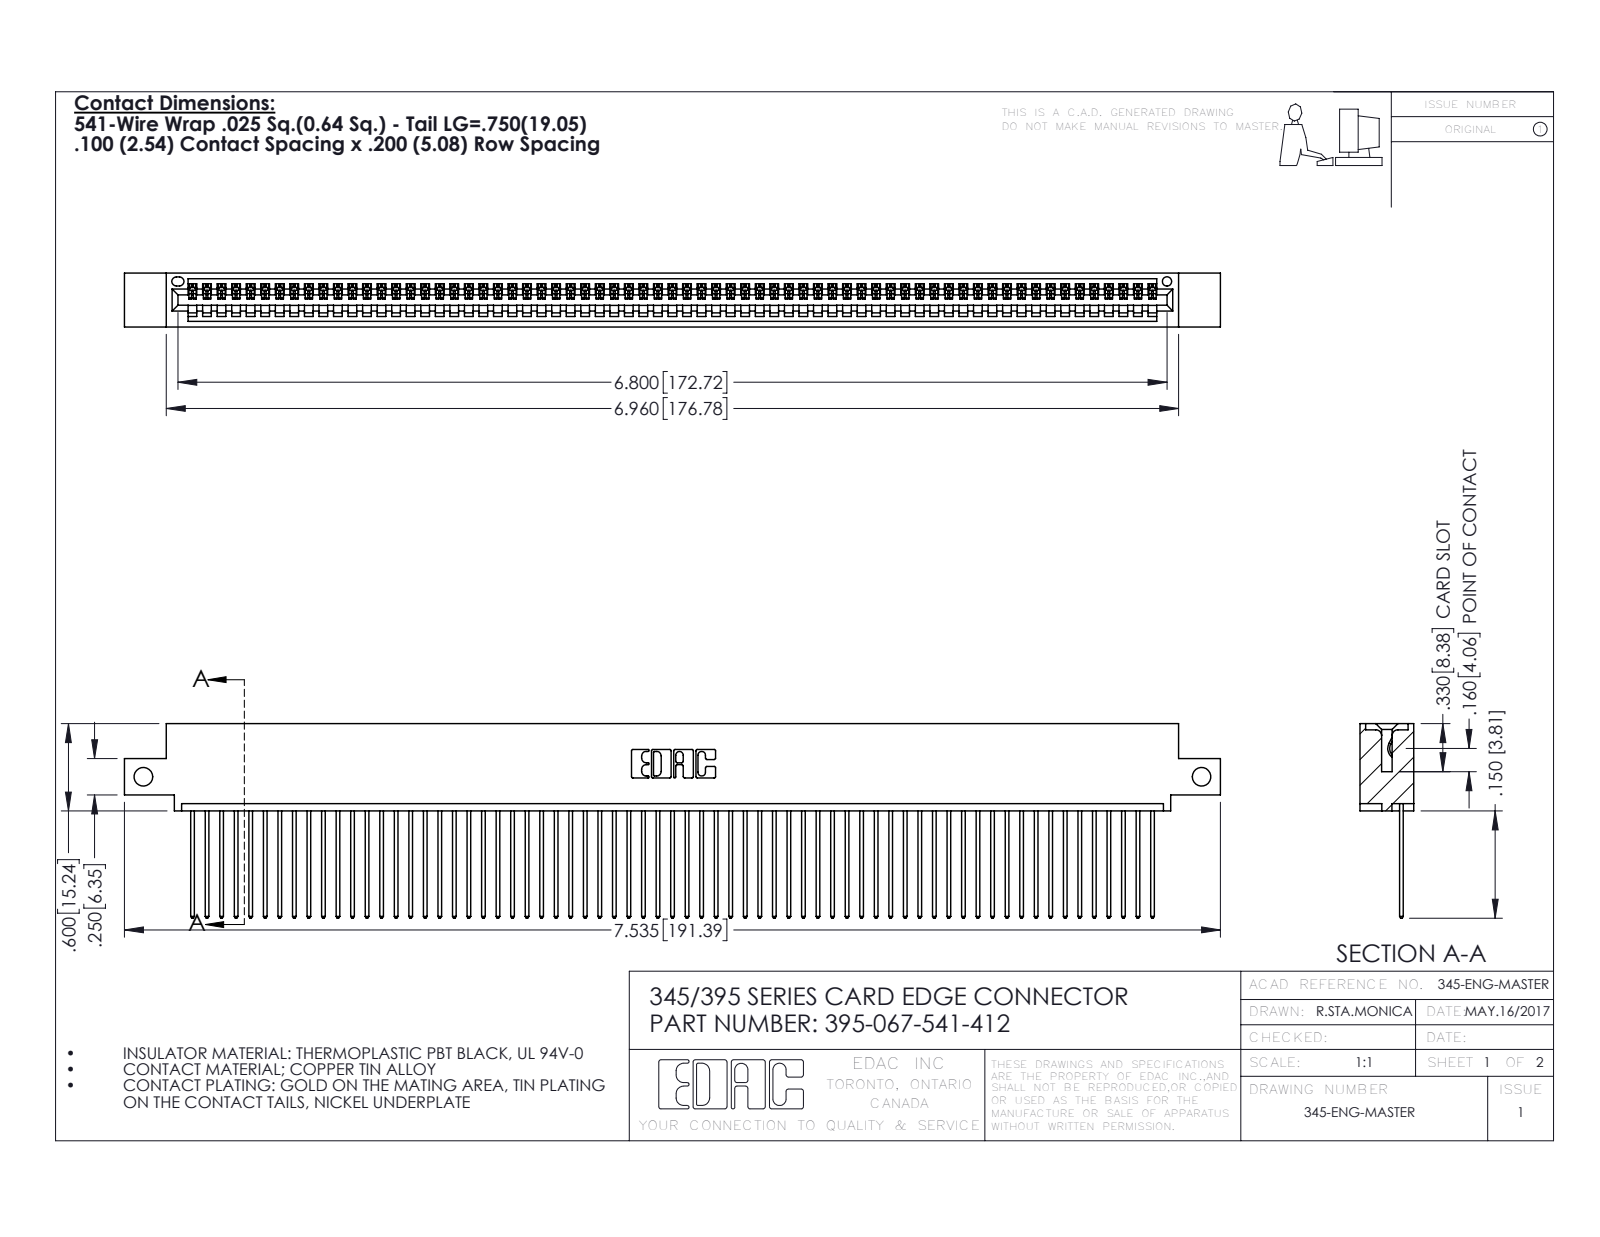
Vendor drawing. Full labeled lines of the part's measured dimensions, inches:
Part name (STEP PRODUCT): 345-292-001_345-293-141; 345 Part_0.110 Offset - Side Mount; 395-067-541-412
STEP written by: SolidWorks 2016 (CONFIG_CONTROL_DESIGN)
Units: inches
Bodies: 68 solids, 4016 faces (2764 planar, 1252 cylindrical, 0 other)
Overall size (bounding box): 7.535 × 1.337 × 0.37
Volume: 1.125 in³ · Surface area: 40.44 in²
Round holes (diameter × count): ⌀0.128 ×2, ⌀0.064 ×1
Partial cylindrical surfaces — rounded edges, fillets, slot ends (radius × count): R0.006 ×134, R0.01 ×134, R0.01 ×22, R0.007 ×6, R0.031 ×6, R0.026 ×3, R0.031 ×2, R0.04 ×2
Main face-to-face distances: 0.072, 0.298, 0.098, 0.272, 0.025, 0.37, 0.2, 0.225, 0.149, 0.072
Hole centre spacings: 7.275
